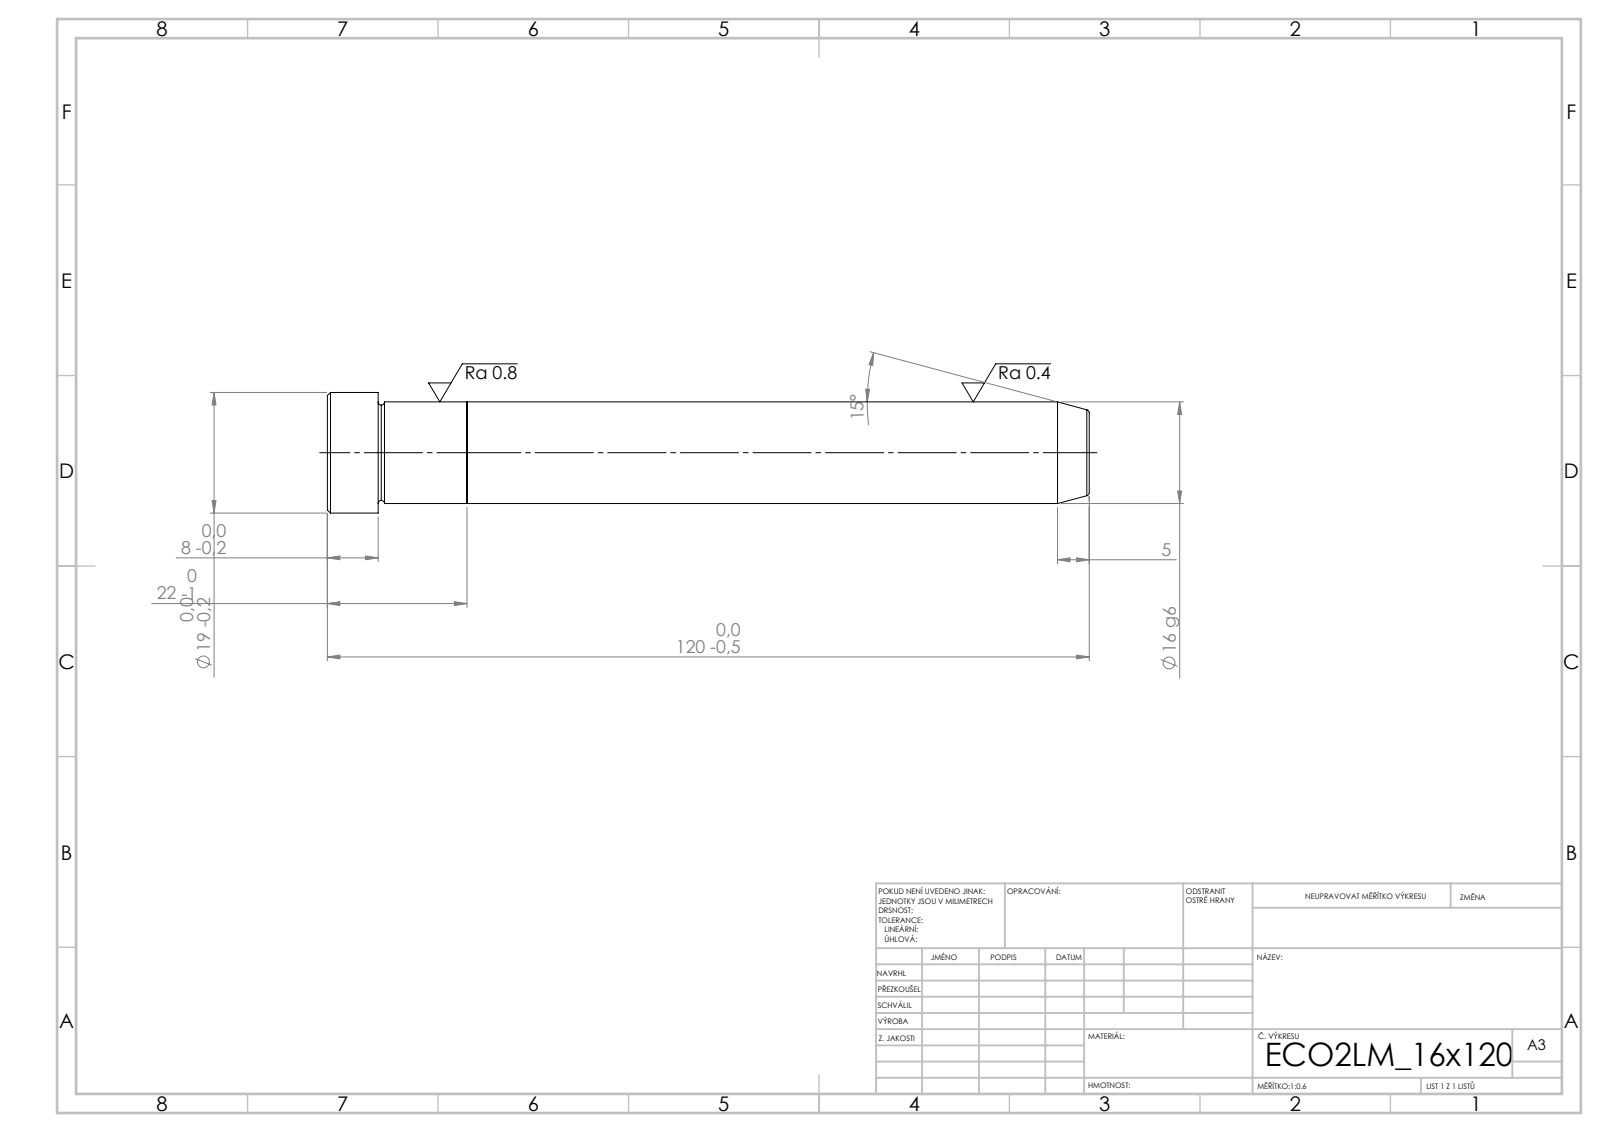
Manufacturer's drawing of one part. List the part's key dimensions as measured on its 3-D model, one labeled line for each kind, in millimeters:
STEP written by: SolidWorks 2019 (CONFIG_CONTROL_DESIGN)
Units: millimetres
Bodies: 2 solids, 21 faces (5 planar, 6 cylindrical, 10 other)
Overall size (bounding box): 120 × 19 × 19
Volume: 24 600 mm³ · Surface area: 7 005 mm²
Round bosses / shafts (diameter × count): ⌀19 ×1, ⌀16 ×1
Main face-to-face distances: 22, 98, 120, 112, 14, 8
